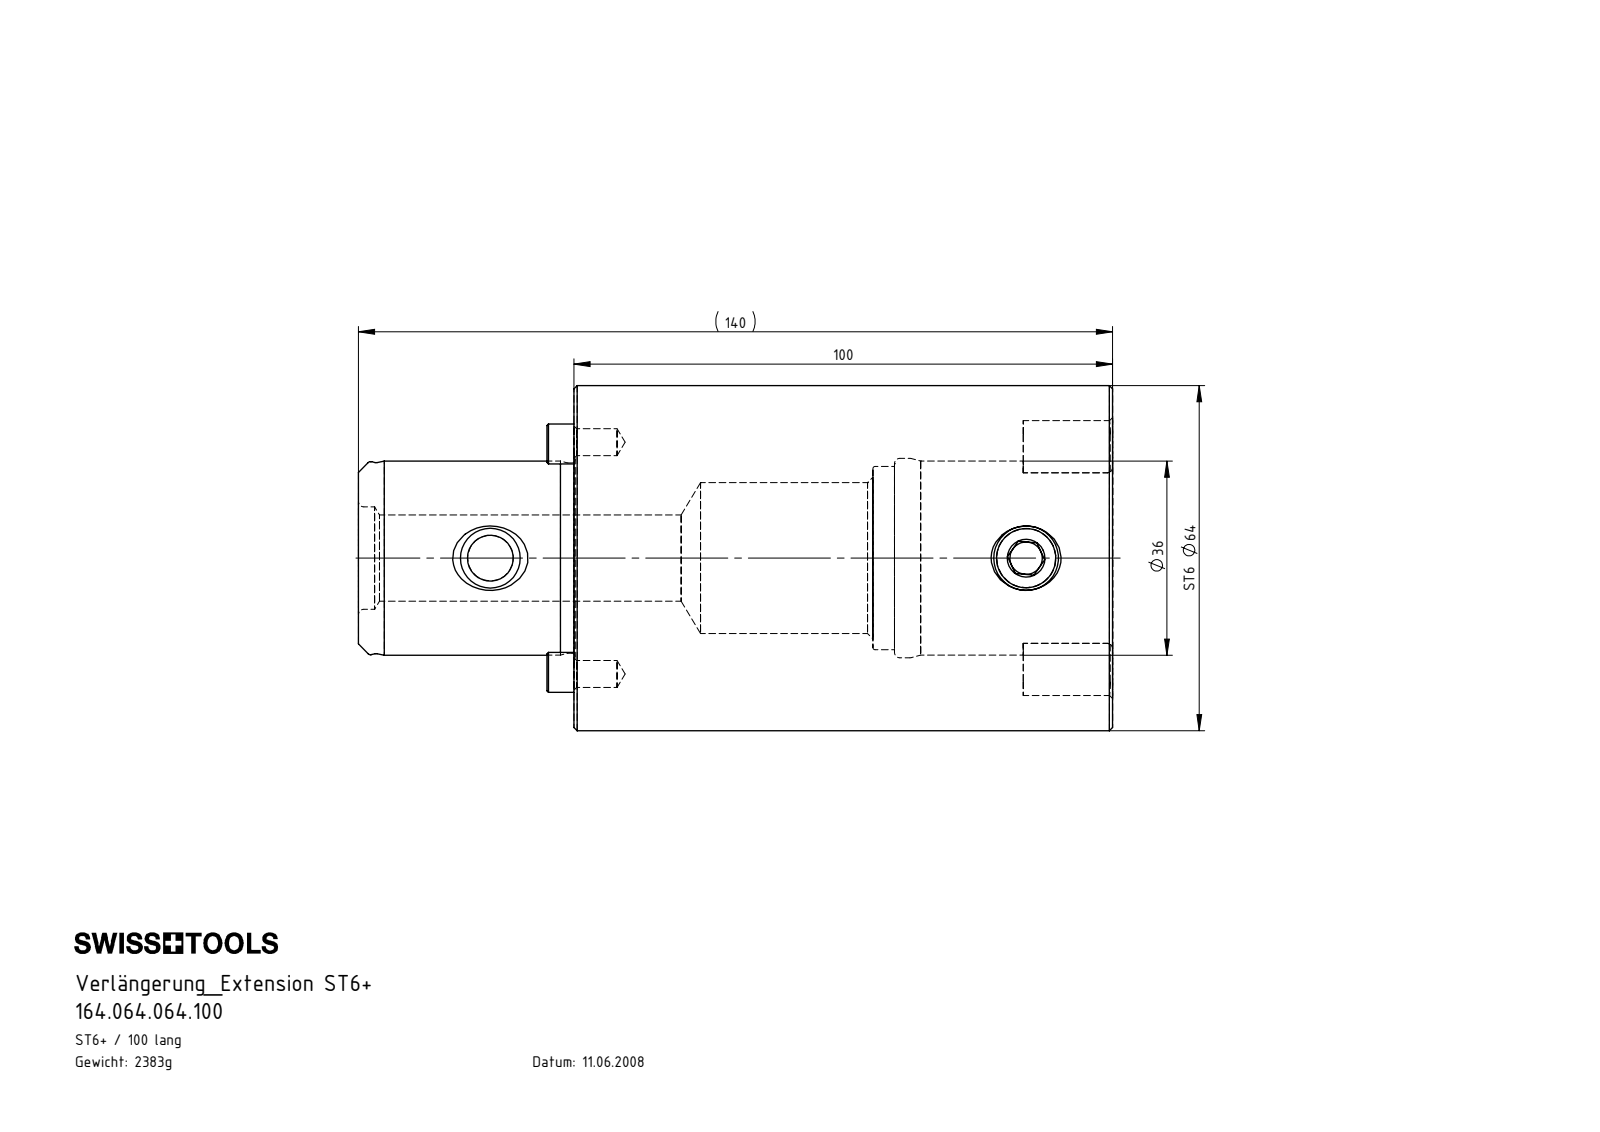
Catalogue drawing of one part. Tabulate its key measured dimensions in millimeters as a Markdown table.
| quantity | value |
| --- | --- |
| part name | ST6-ER3.K01.040_A; ST6-ER2.001.012_A; ST6-ST6.K01.100; ST6-ST6.K01.100_A (+3 more) |
| STEP written by | SolidWorks 2015 (CONFIG_CONTROL_DESIGN) |
| units | millimeters |
| bodies | 7 solids, 237 faces (46 planar, 78 cylindrical, 113 other) |
| overall size | 140 × 64 × 64 |
| volume | 303 943 mm³ |
| surface area | 54 822 mm² |
| round holes (diameter × count) | 5 × 2, 8.5 × 2, 11 × 1, 16 × 1, 18.5 × 1, 19 × 1, 28 × 1, 34 × 1, 36 × 1, 37 × 1 |
| round bosses / shafts (diameter × count) | 64 × 1, 35.8 × 1, 35.3 × 1, 33.5 × 1, 30 × 1, 27 × 1, 18 × 1, 12 × 1 |
| partial cylindrical surfaces (radius × count) | 1.6 × 6, 4.5 × 6, 0.5 × 4, 5.2 × 2, 5.47 × 2, 18.05 × 2 |
| main face-to-face distances | 100, 20, 60.5, 59.5, 40.5, 40, 79.5, 39.5, 44.5, 99.5 |
| hole center spacings | 21.5, 43, 99.45 |
